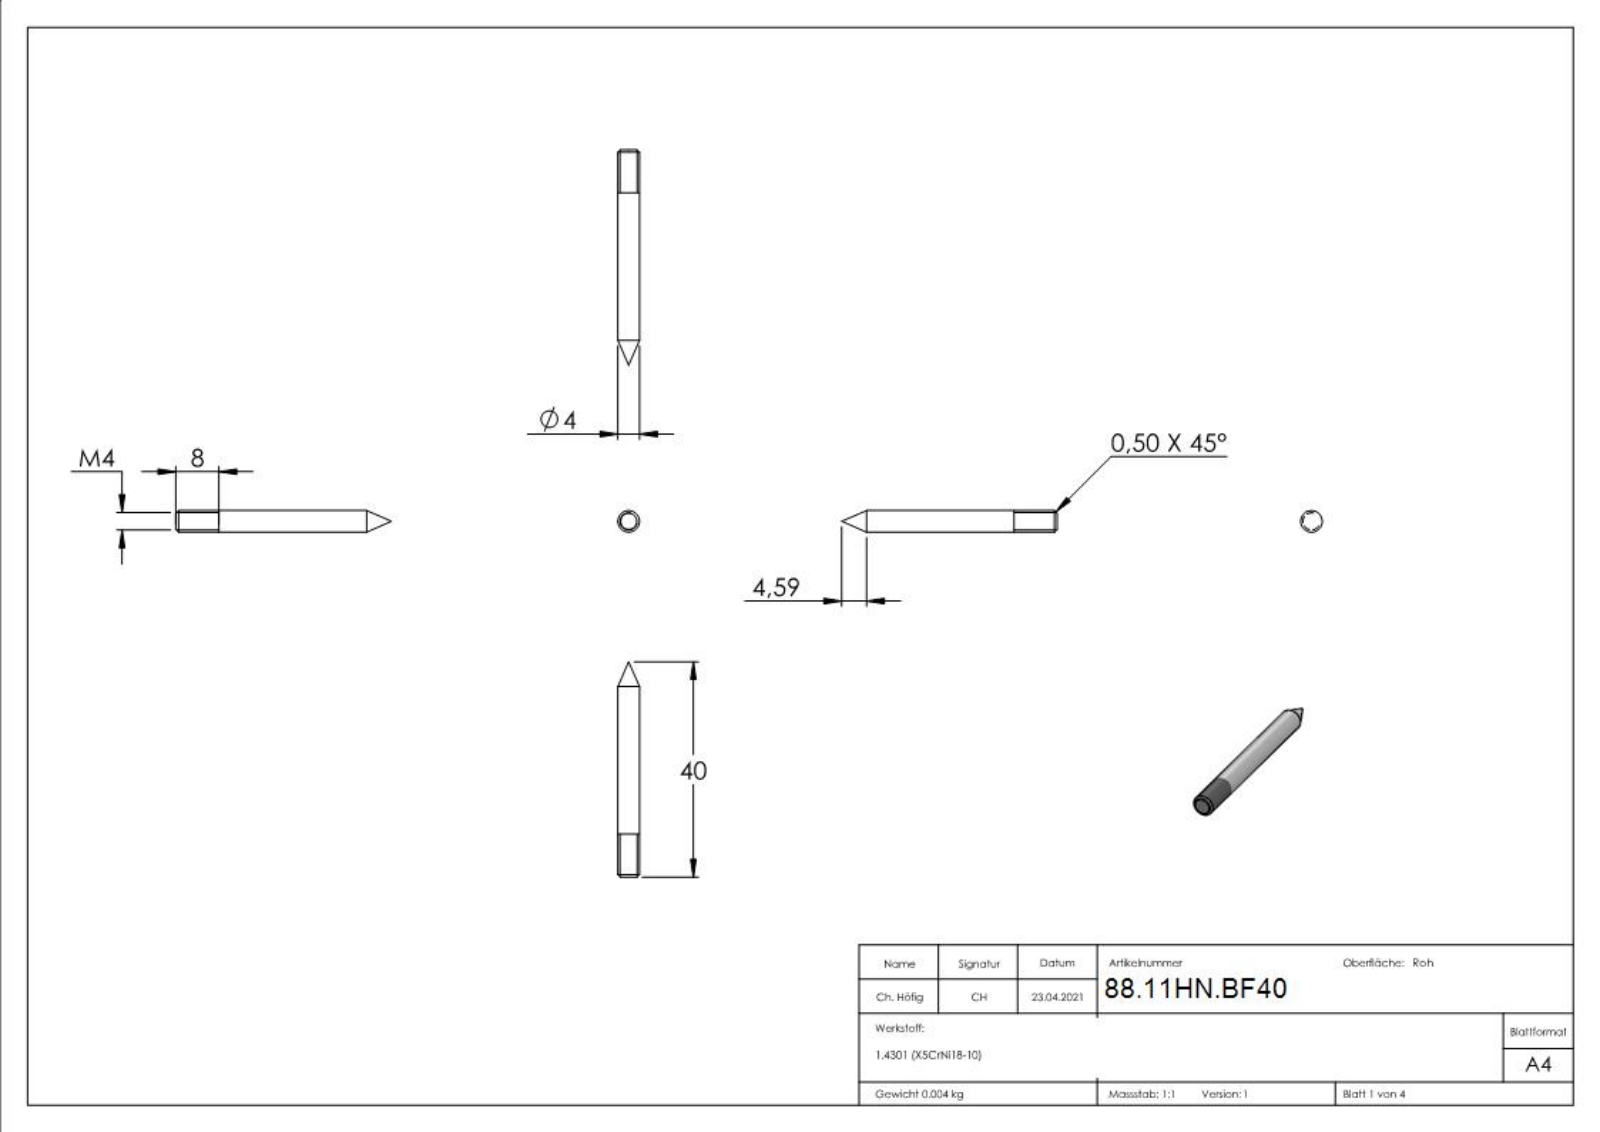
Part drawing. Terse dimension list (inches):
name: 040-HN-X Teil3; 040-HN-X Teil4_040-HN-X Teil4; 040-HN-X Teil2; 040-HN-X Teil3_040-HN-X Teil3 (+3 more)
written by: SolidWorks 2018 (CONFIG_CONTROL_DESIGN)
unit: in
bodies: 6 solids, 1310 faces (226 planar, 366 cylindrical, 718 other)
size: 393.701 × 205.411 × 181.413
volume: 0.137 in³; area: 5.964 in²
holes: 2× ⌀0.169
bosses: 2× ⌀0.472, 2× ⌀0.315, 2× ⌀0.236, 2× ⌀0.22, 2× ⌀0.181, 2× ⌀0.157
rounds: 24× R0.004, 2× R0.138
face distances: 0.043, 0.039, 0.354, 0.348, 0.02, 0.024, 1.417, 1.398, 1.374, 0.394
hole spacings: 0.551
